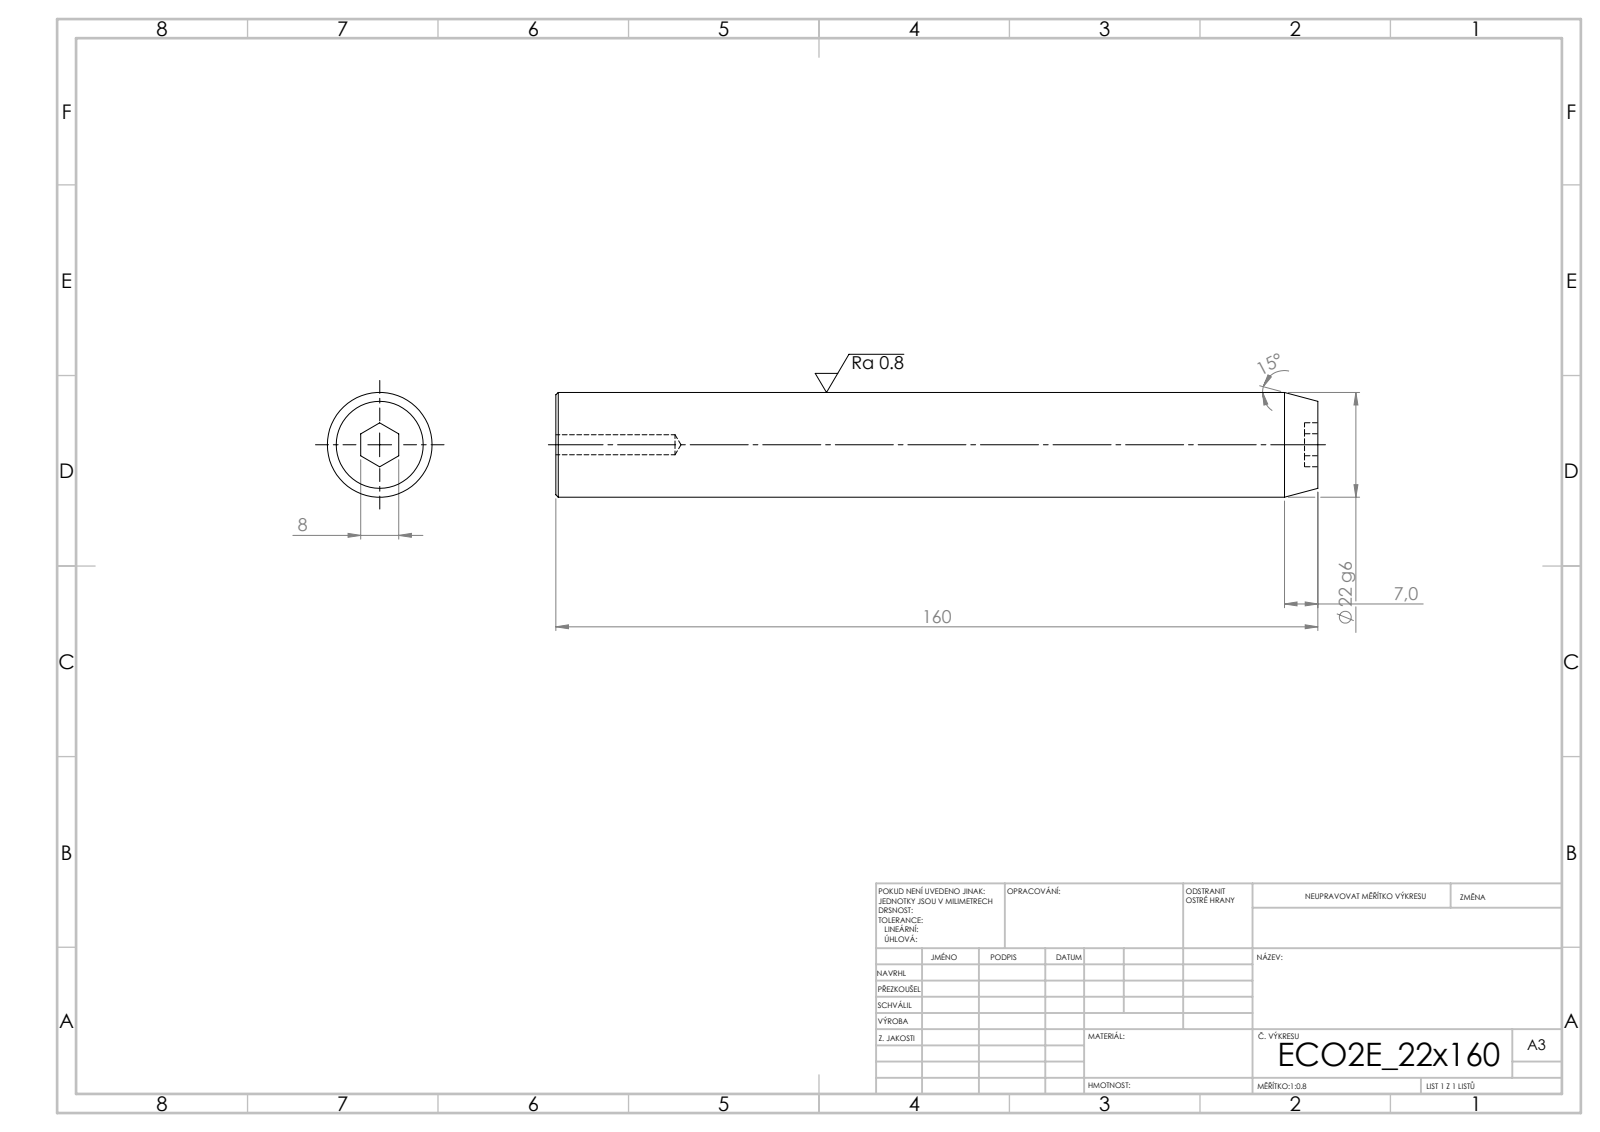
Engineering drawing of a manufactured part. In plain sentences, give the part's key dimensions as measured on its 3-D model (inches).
Its 3-D file was written by "SolidWorks 2019 (CONFIG_CONTROL_DESIGN)". It is 1 solid with 19 faces: 9 planar, 4 cylindrical and 6 other. Overall it measures 6.299 by 0.866 by 0.866 inches. Its volume is 3.654 cubic inches and its surface area 18.7 square inches. Round holes: 1 of diameter 0.165. Round bosses or shafts: 1 of diameter 0.866. The main face-to-face distances are 6.299, 0.11, 6.189, 0.315.
